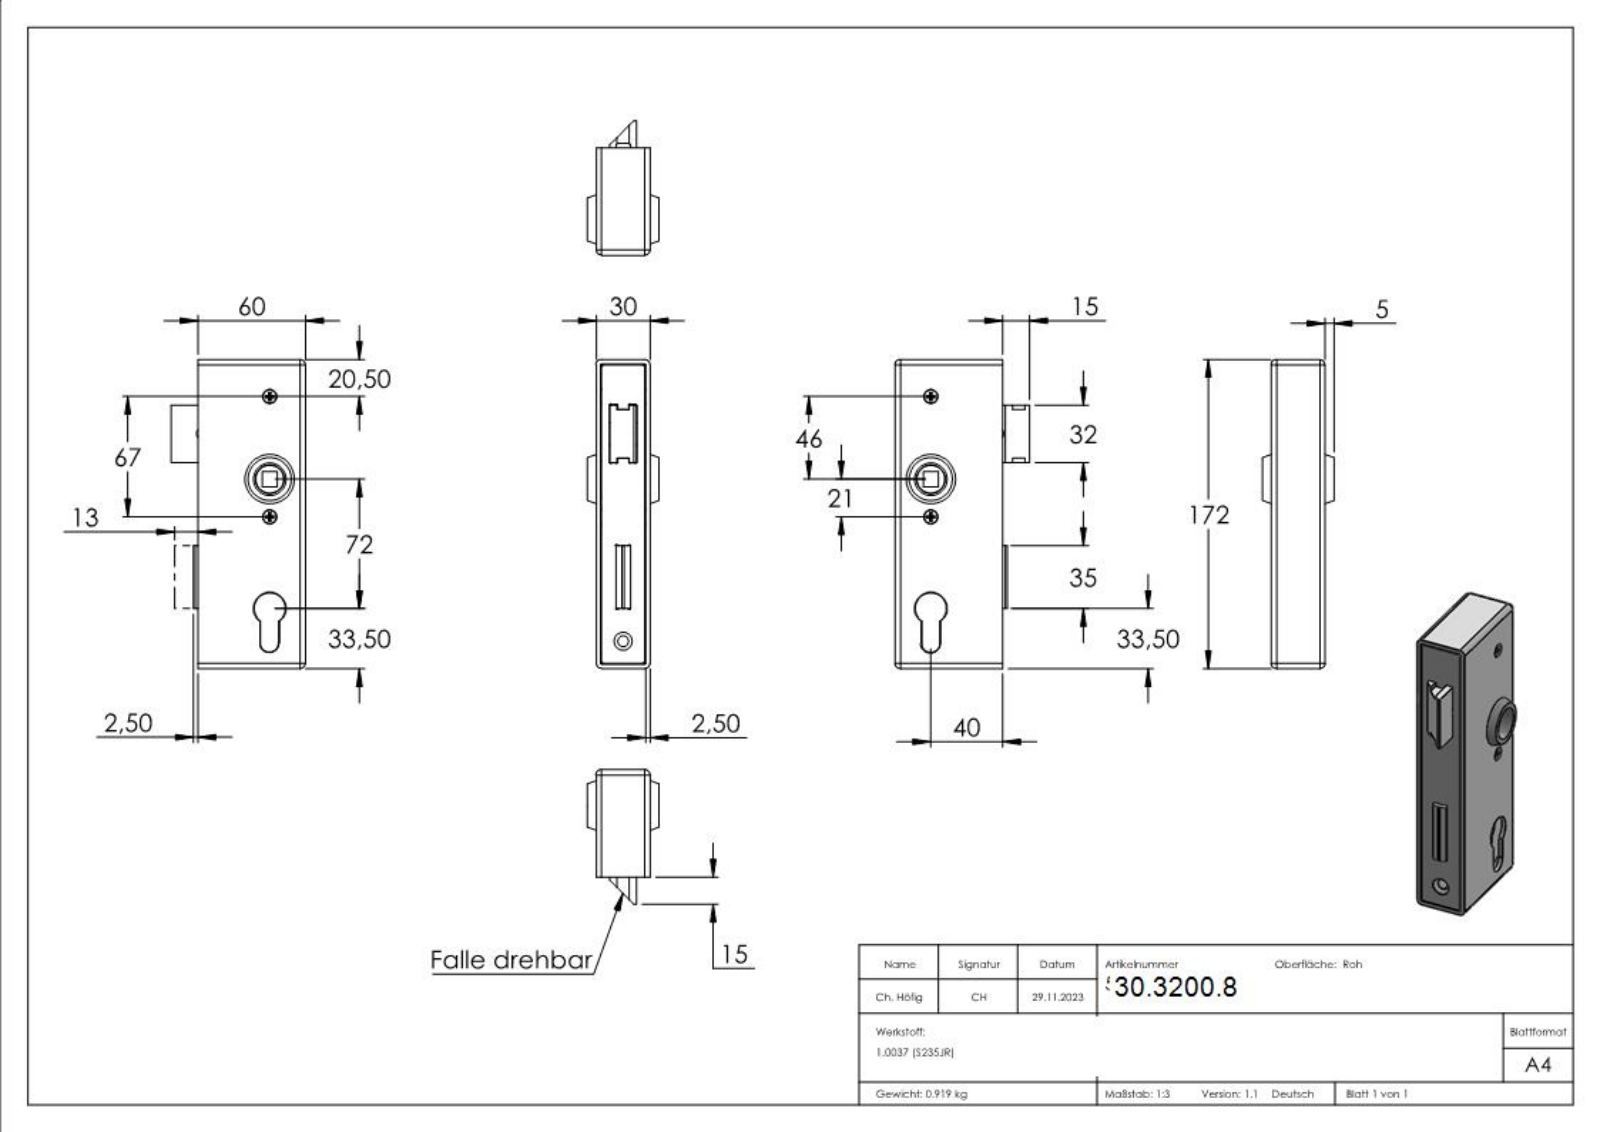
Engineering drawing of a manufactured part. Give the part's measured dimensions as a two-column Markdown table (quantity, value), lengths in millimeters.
| quantity | value |
| --- | --- |
| part name | 59100-ST; Schlosskasten Teil4 Konfig_59XXX-240 Teil4; Schlosskasten Teil6 Konfig_59100-240 Teil6; Schlosskasten Teil5 Konfig_59XXX-240 Teil5 (+4 more) |
| STEP written by | SolidWorks 2018 (CONFIG_CONTROL_DESIGN) |
| units | millimeters |
| bodies | 15 solids, 366 faces (210 planar, 117 cylindrical, 39 other) |
| overall size | 172 × 75 × 40 |
| volume | 118 746 mm³ |
| surface area | 107 830 mm² |
| round holes (diameter × count) | 3.5 × 5, 8 × 4, 3.3 × 2, 4.3 × 2, 6 × 1, 10 × 1, 16 × 1, 17.3 × 1, 18.15 × 1, 20.5 × 1 |
| round bosses / shafts (diameter × count) | 7.2 × 2, 4 × 2, 3.6 × 2, 20 × 1, 17 × 1, 15.5 × 1 |
| partial cylindrical surfaces (radius × count) | 0.5 × 12, 0.3 × 8, 0.6 × 8, 3 × 8, 1 × 4, 4.39 × 4, 7.5 × 4, 8 × 4 |
| main face-to-face distances | 2.5, 27.5, 23.5, 21, 4, 8.25, 21.75, 5.75, 19.25, 6.5 |
| hole center spacings | 13.15, 13.9, 14.42, 18, 19.91, 21, 27.66, 27.77 |
